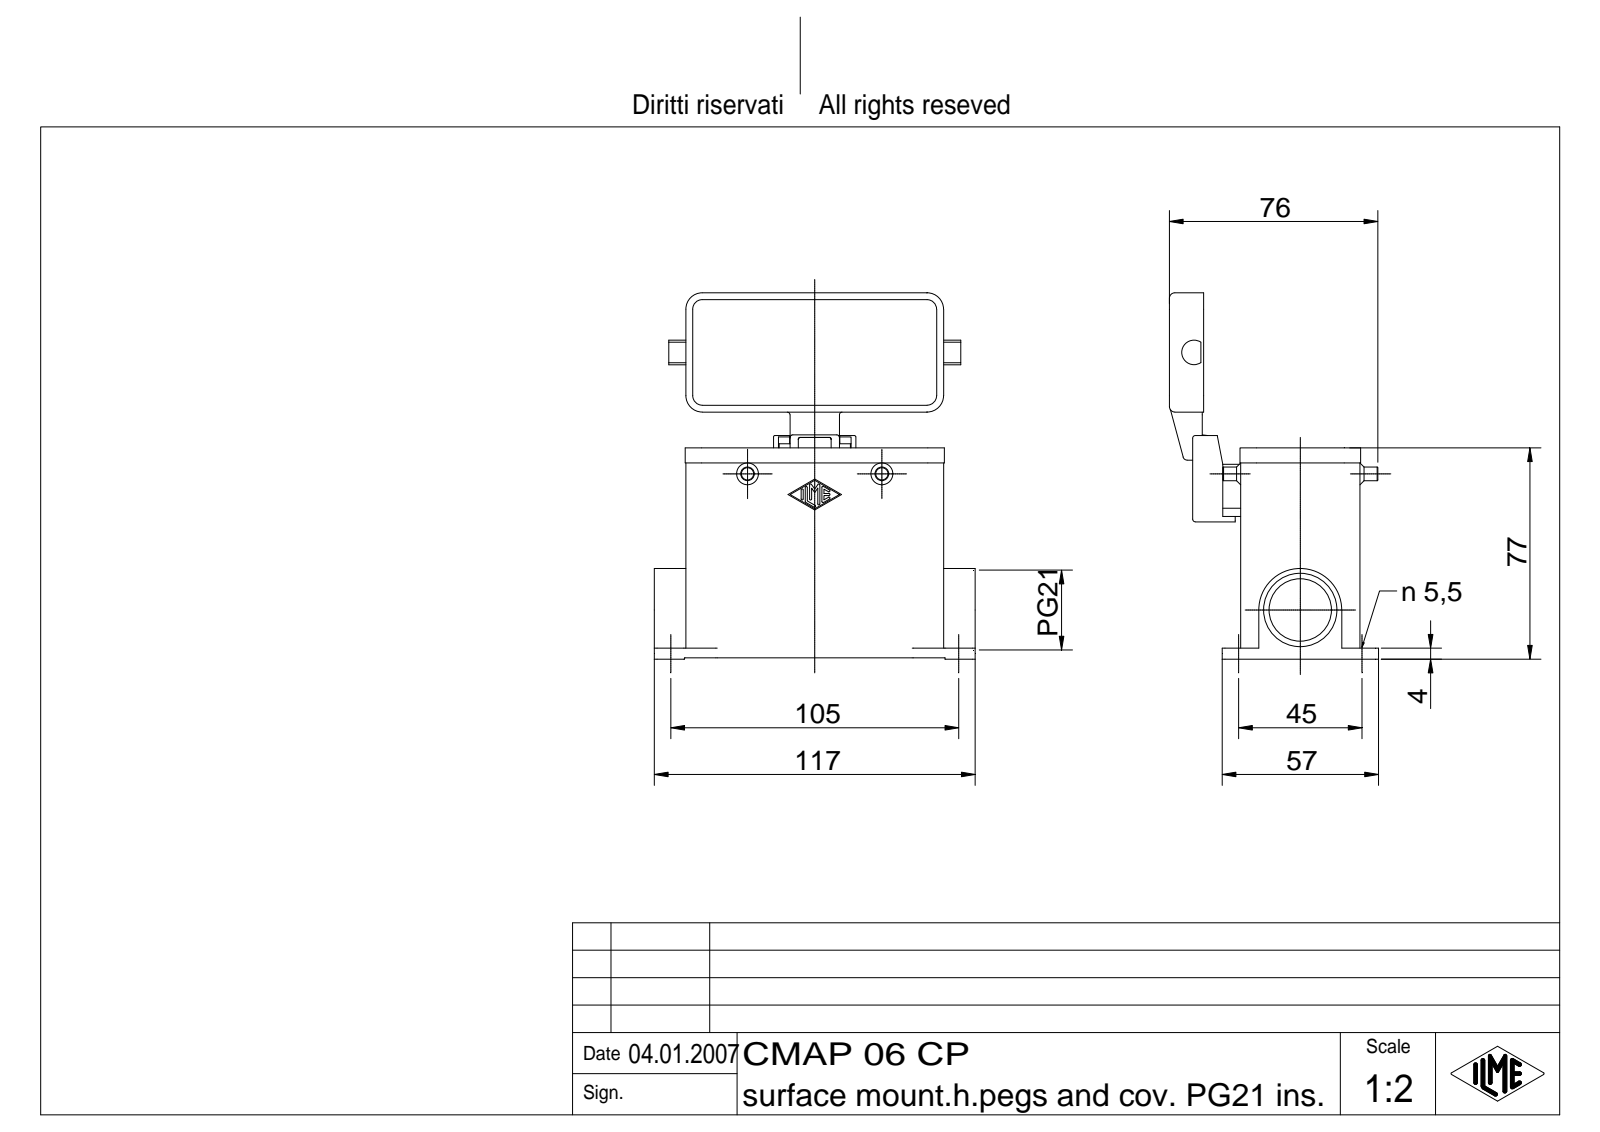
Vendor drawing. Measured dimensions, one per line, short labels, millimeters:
name: CMAP 06 CP
written by: Autodesk Inventor 7 (AUTOMOTIVE_DESIGN)
unit: mm
bodies: 2 solids, 471 faces (173 planar, 177 cylindrical, 121 other)
size: 133.5 × 117 × 76.25
volume: 136 209 mm³; area: 72 907 mm²
holes: 4× ⌀5.5, 1× ⌀4, 1× ⌀5, 1× ⌀22.78, 1× ⌀26.78
bosses: 2× ⌀5, 2× ⌀3, 1× ⌀7, 1× ⌀4
rounds: 26× R1, 14× R0.38, 12× R6, 9× R0.5, 8× R0.7, 8× R2, 4× R3, 4× R3.5
face distances: 3, 40.5, 43.5, 3.5, 37.5, 29, 22.5, 69.5, 66.5, 26
hole spacings: 45, 105, 114.24
